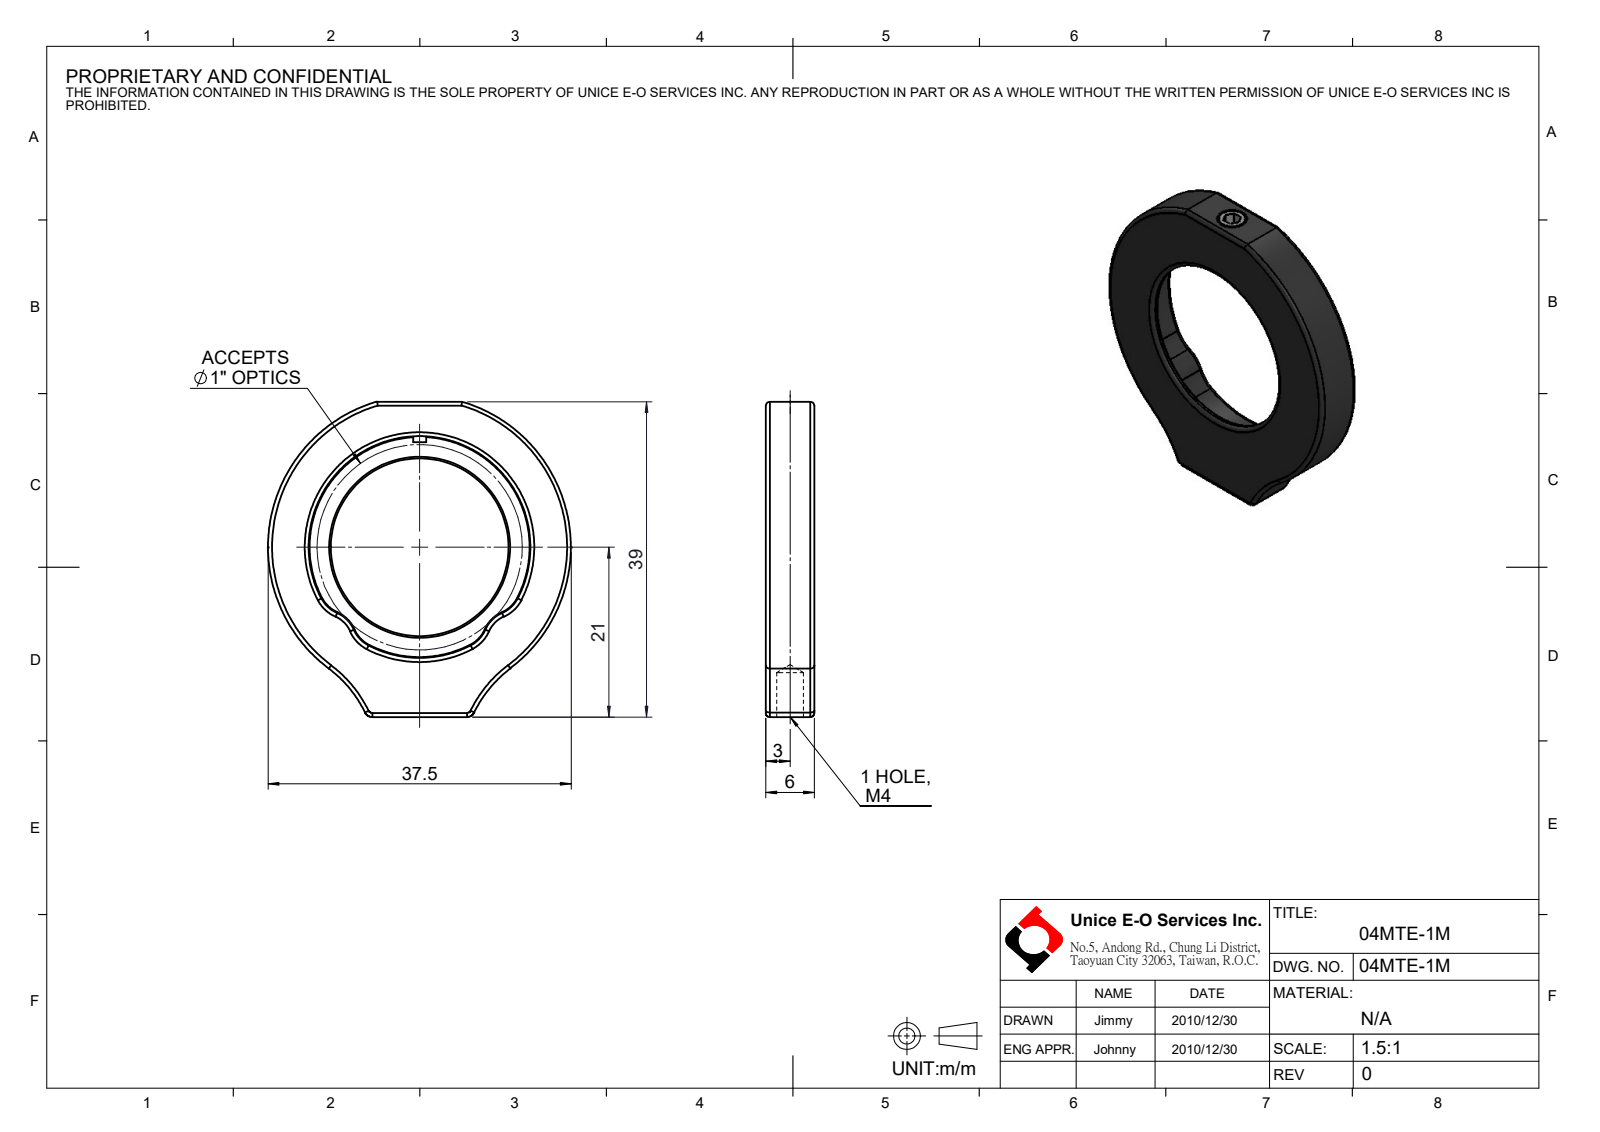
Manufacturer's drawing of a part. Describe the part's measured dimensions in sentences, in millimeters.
The part is named "04MTE-1M". Its 3-D file was written by "SolidWorks 2016 (CONFIG_CONTROL_DESIGN)". It is 3 solids with 95 faces: 16 planar, 33 cylindrical and 46 other. Overall it measures 39 by 37.5 by 6 millimeters. Its volume is 3 503 cubic millimeters and its surface area 2 855 square millimeters. Round holes: 1 of diameter 1.5, 1 of diameter 3.3, 1 of diameter 22, 1 of diameter 27.4. Round bosses or shafts: 1 of diameter 4, 1 of diameter 1.6. Partial cylindrical surfaces (rounded edges, fillets, slot ends): 6 of radius 4, 4 of radius 0.5, 2 of radius 1, 2 of radius 15, 1 of radius 18.75. The main face-to-face distances are 6, 1, 5, 39, 2, 35, 4, 2.5, 36.5, 1.5.
